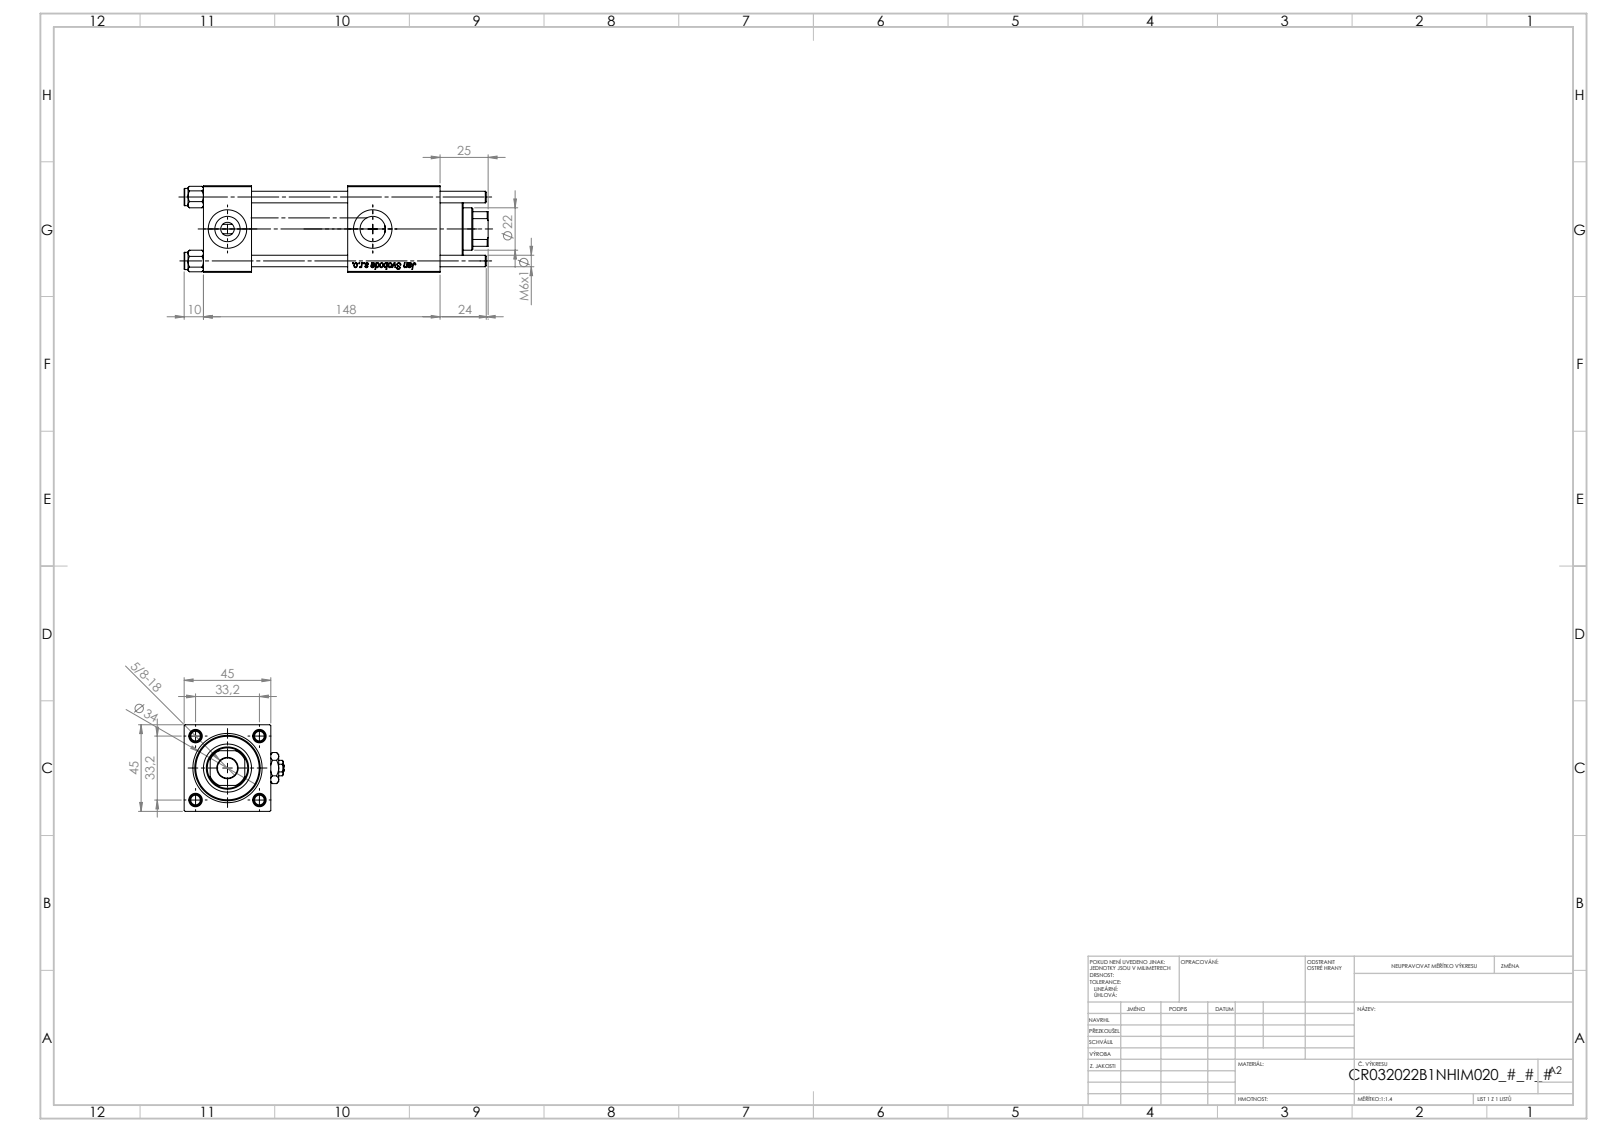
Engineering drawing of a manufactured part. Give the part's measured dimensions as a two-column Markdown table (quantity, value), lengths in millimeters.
| quantity | value |
| --- | --- |
| part name | V215_VC_A; V215CR_VCP_B; Zatka_pro_OIL_PORT; NUT_M5_B (+2 more) |
| STEP written by | SolidWorks 2019 (CONFIG_CONTROL_DESIGN) |
| units | millimeters |
| bodies | 12 solids, 1205 faces (455 planar, 82 cylindrical, 668 other) |
| overall size | 158 × 52 × 45 |
| volume | 213 630 mm³ |
| surface area | 77 550 mm² |
| round holes (diameter × count) | 6 × 4, 7 × 2, 13.16 × 2, 20 × 2, 10.5 × 1, 22 × 1, 24 × 1, 25 × 1, 32 × 1, 33 × 1 |
| round bosses / shafts (diameter × count) | 9 × 4, 38 × 1, 34 × 1 |
| partial cylindrical surfaces (radius × count) | 10.5 × 1 |
| main face-to-face distances | 45, 25, 50, 123, 75, 98, 48, 94.3, 69.3, 19.3 |
| hole center spacings | 23.48, 33.2, 46.95, 75.5 |
